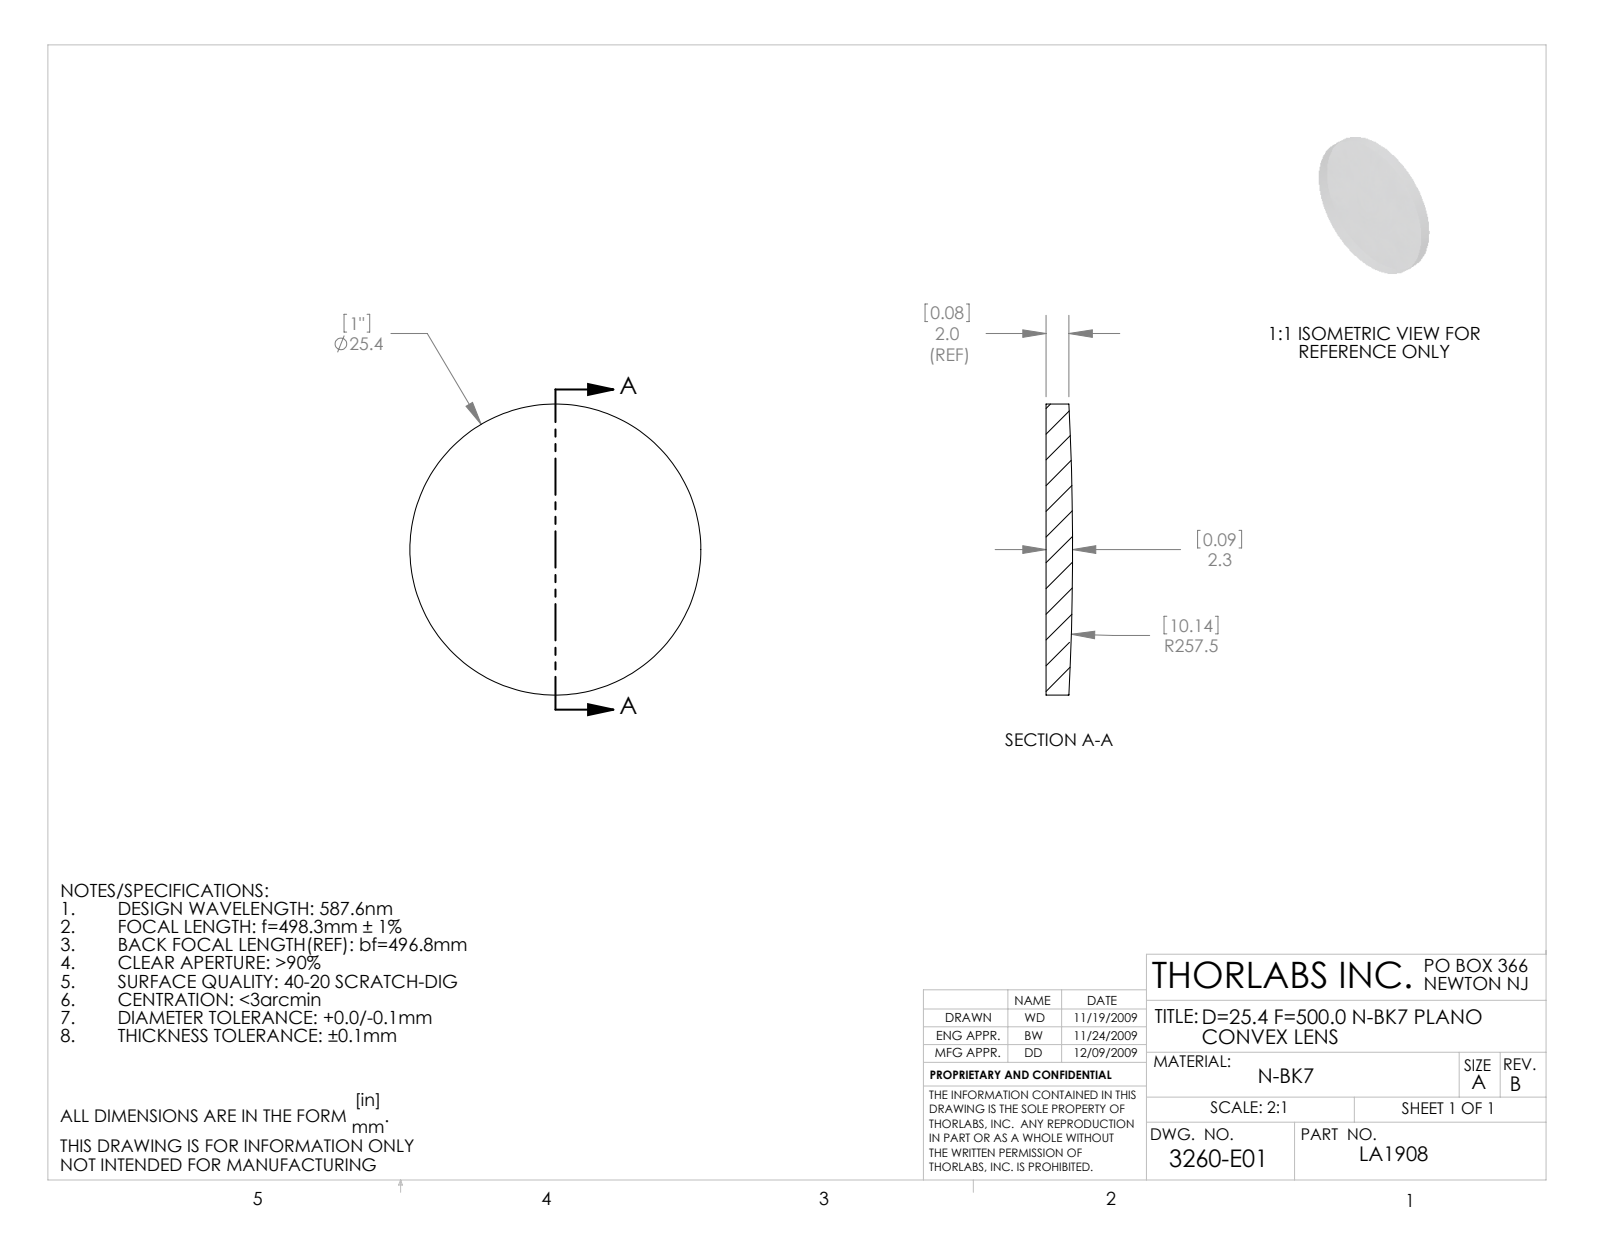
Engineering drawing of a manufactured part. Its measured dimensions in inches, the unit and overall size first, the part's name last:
Units: inches
Overall size (bounding box): 1 × 1 × 0.091
Round bosses / shafts (diameter × count): ⌀1 ×1
Volume: 0.067 in³ · Surface area: 1.818 in²
Bodies: 1 solid, 5 faces (1 planar, 2 cylindrical, 2 other)
Part name (STEP PRODUCT): 3260-E0W
STEP written by: SolidWorks 2009 (AUTOMOTIVE_DESIGN)
